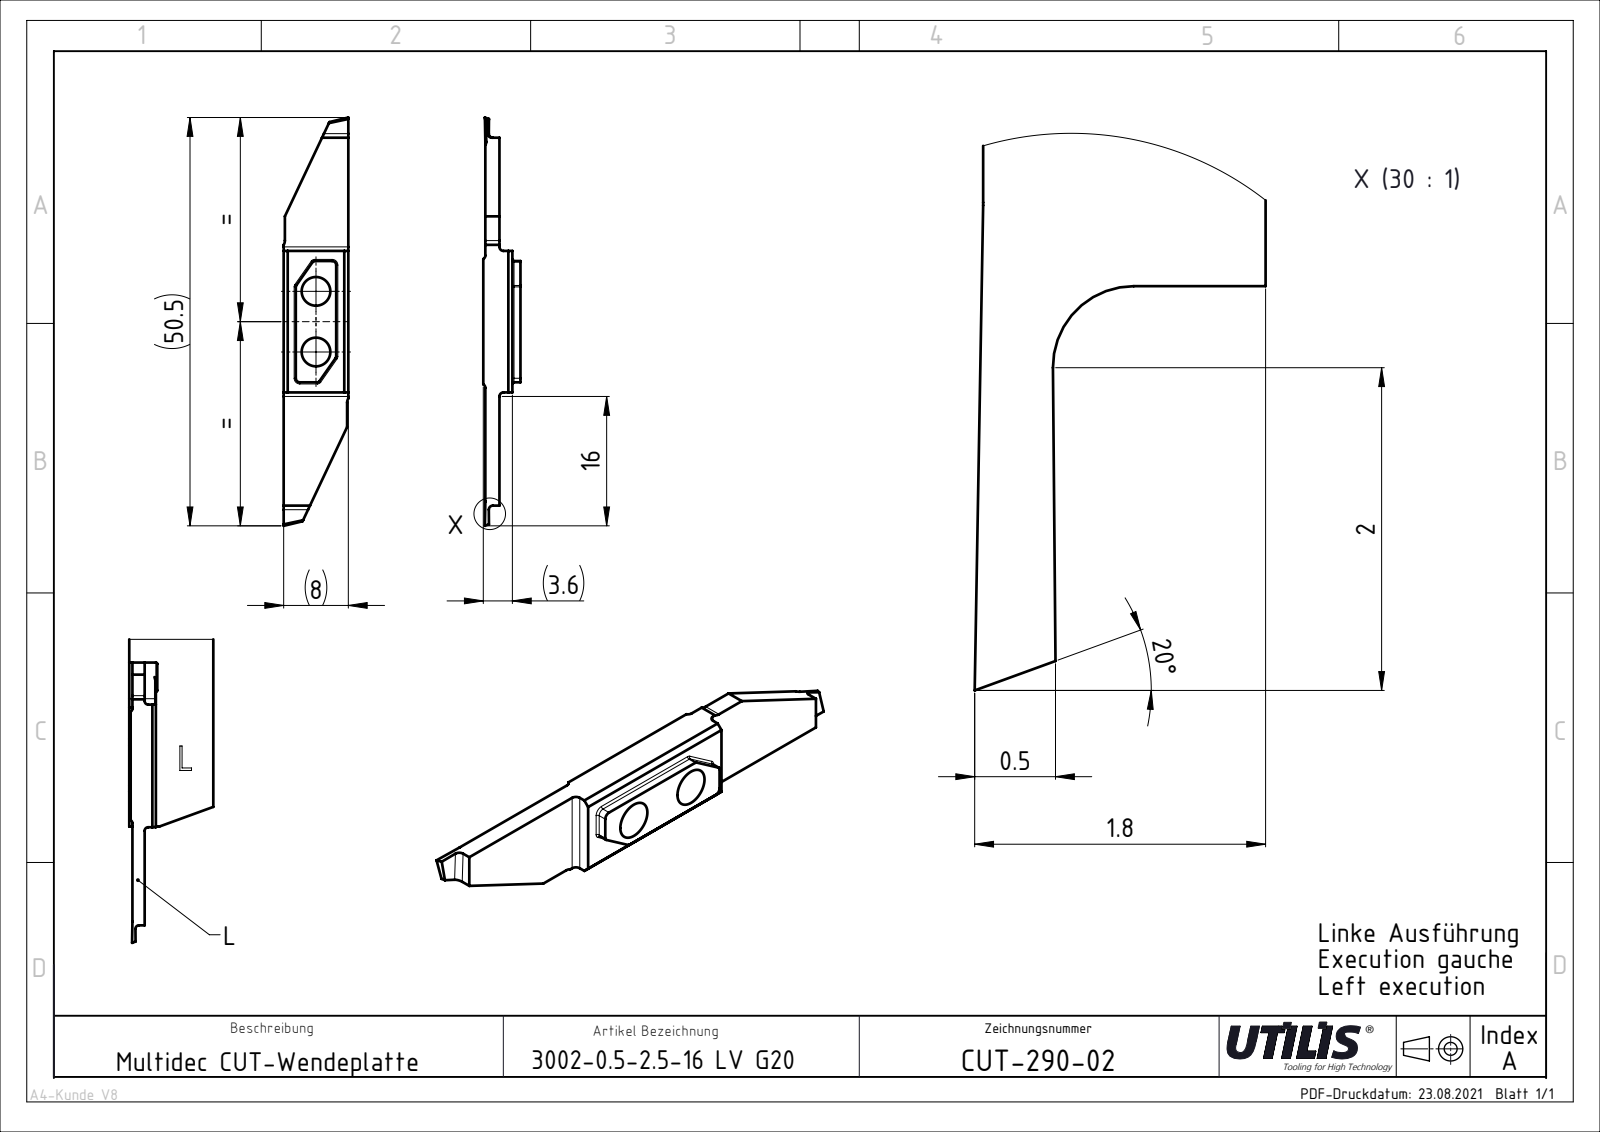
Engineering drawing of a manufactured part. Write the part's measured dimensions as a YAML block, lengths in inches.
part_name: "CUT-290-02"
step_written_by: "SolidWorks 2016 (AUTOMOTIVE_DESIGN)"
units: inches
bodies: {solids: 1, faces: 38, planar: 24, cylindrical: 14, other: 0}
overall_size: [1.988, 0.315, 0.14]
volume: 0.045
surface_area: 1.48
round_holes:
  - {diameter: 0.14, count: 2}
partial_cylinders:
  - {radius: 0.02, count: 6}
  - {radius: 0.006, count: 2}
  - {radius: 0.039, count: 2}
face_to_face_distances: [0.069, 0.13, 0.061, 0.079, 0.14, 0.315, 0.713, 0.309, 0.689, 0.303]
hole_center_spacings: [0.295]
